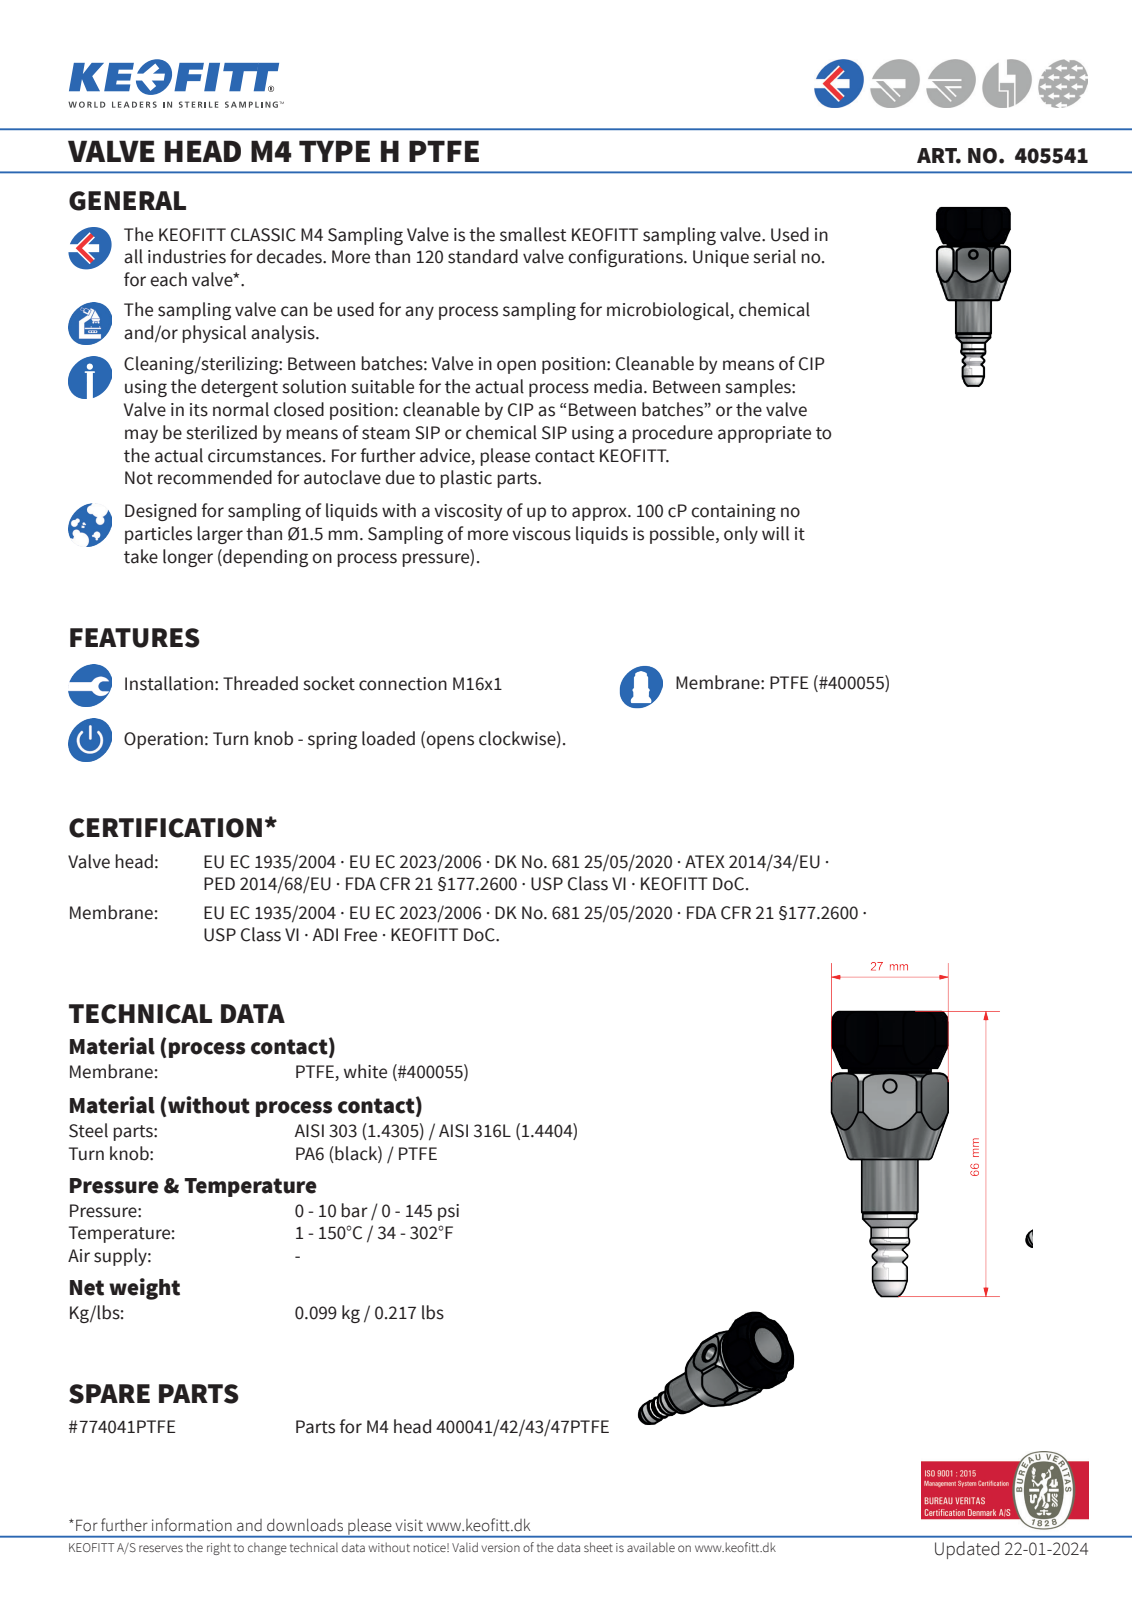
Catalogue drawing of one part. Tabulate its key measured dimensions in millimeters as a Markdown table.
| quantity | value |
| --- | --- |
| STEP written by | Autodesk Inventor 2008 (AUTOMOTIVE_DESIGN) |
| units | millimeters |
| bodies | 1 solid, 115 faces (23 planar, 40 cylindrical, 52 other) |
| overall size | 66.11 × 28 × 26.97 |
| volume | 17 980 mm³ |
| surface area | 6 083 mm² |
| round holes (diameter × count) | 3.05 × 1, 6.1 × 1, 6.97 × 1, 10.2 × 1, 12 × 1, 14.4 × 1, 14.92 × 1, 15 × 1, 16.5 × 1 |
| round bosses / shafts (diameter × count) | 19 × 1, 16 × 1, 13 × 1, 12.5 × 1, 11.92 × 1, 11 × 1, 10 × 1, 8.6 × 1 |
| partial cylindrical surfaces (radius × count) | 6 × 6, 1.75 × 1, 4.64 × 1, 13.48 × 1, 14 × 1 |
| main face-to-face distances | 24, 13.8, 1.11, 12.69, 14.31, 13.2, 0.51, 0.31, 0.8, 13.49 |
| hole center spacings | 2 |
